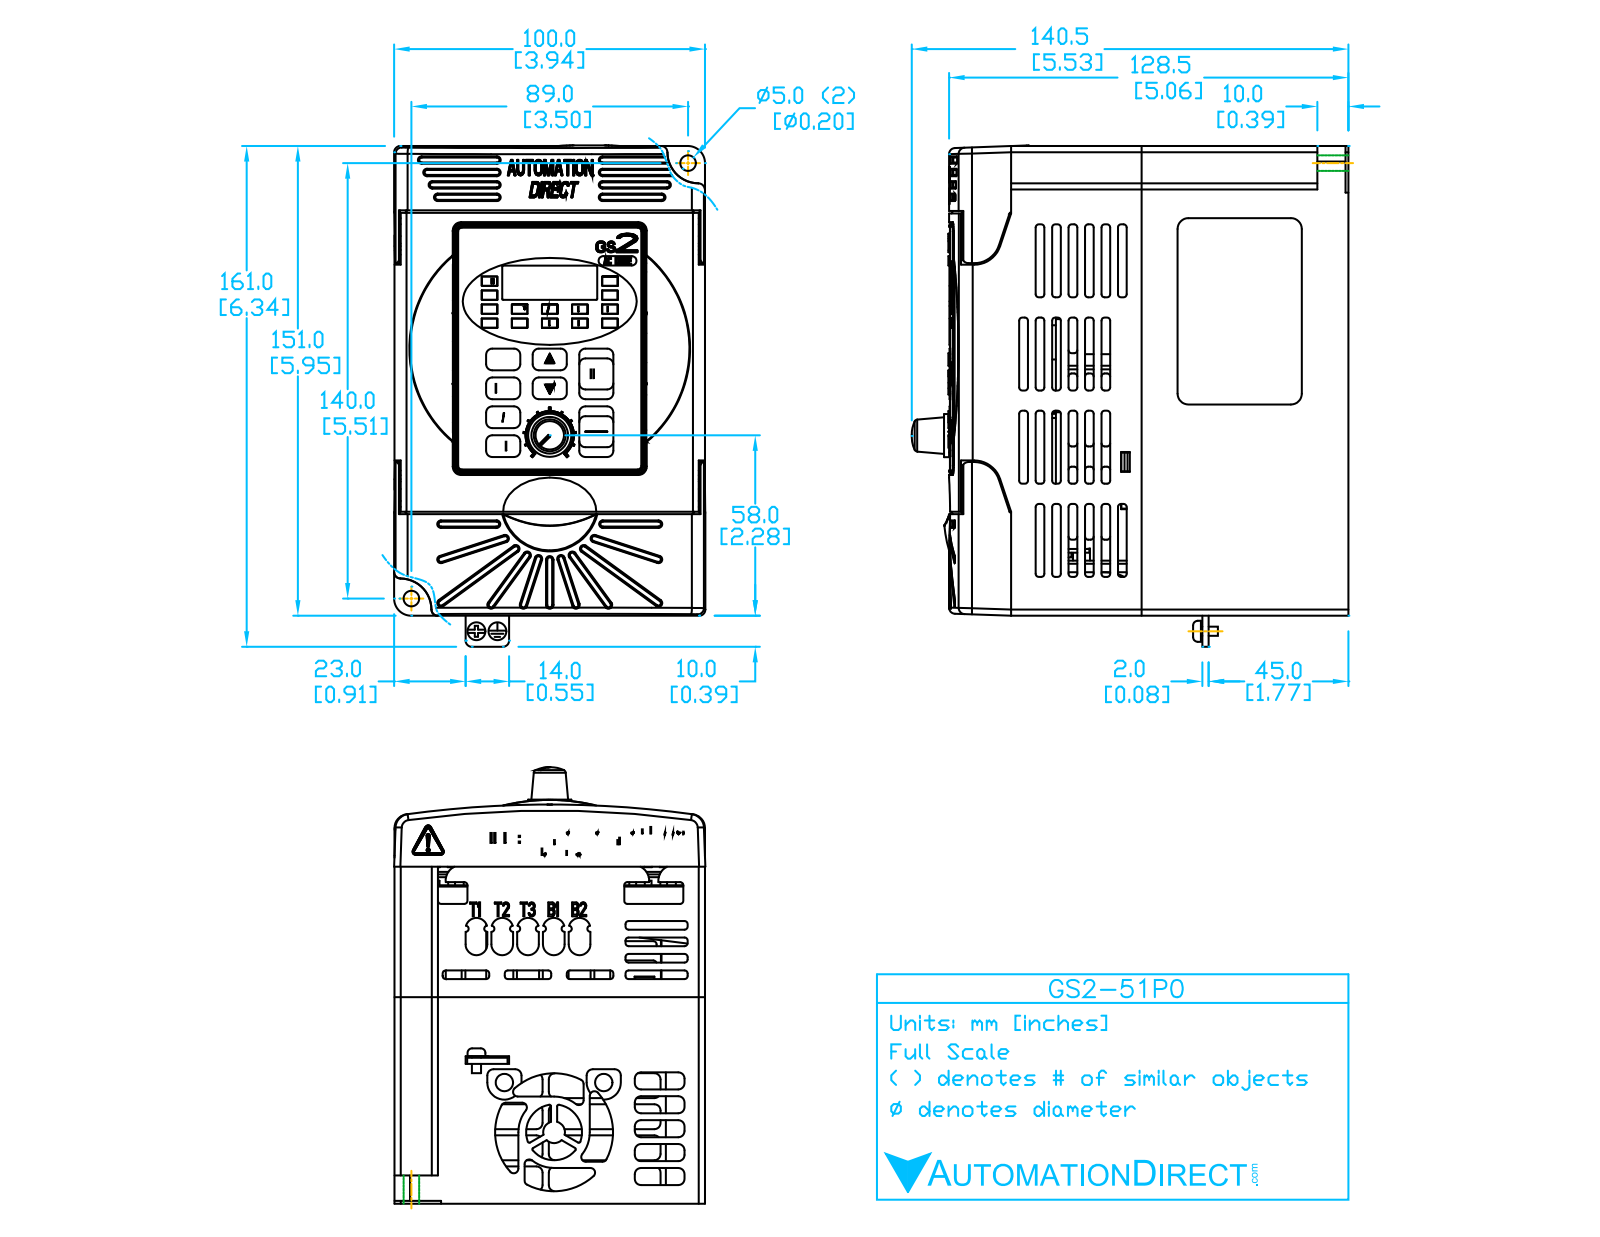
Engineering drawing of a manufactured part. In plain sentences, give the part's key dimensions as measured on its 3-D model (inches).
The part is named "GS2-51P0". Its 3-D file was written by "SolidWorks 2015 (AUTOMOTIVE_DESIGN)". It is 1 solid with 735 faces: 316 planar, 228 cylindrical and 191 other. Overall it measures 6.345 by 5.495 by 3.94 inches. Its volume is 112.9 cubic inches and its surface area 196.7 square inches. Round holes: 2 of diameter 0.2, 1 of diameter 0.7, 1 of diameter 1.46. Round bosses or shafts: 1 of diameter 0.545, 1 of diameter 0.22, 1 of diameter 0.15. Partial cylindrical surfaces (rounded edges, fillets, slot ends): 40 of radius 0.04, 24 of radius 0.06, 10 of radius 0.125, 8 of radius 0.02, 8 of radius 0.03, 6 of radius 0.045, 6 of radius 0.2, 4 of radius 0.1. The main face-to-face distances are 3.94, 5.95, 4.256, 4.266, 0.015, 5.935, 0.03, 0.761, 3.179, 0.03. The hole center spacings are 6.528.
